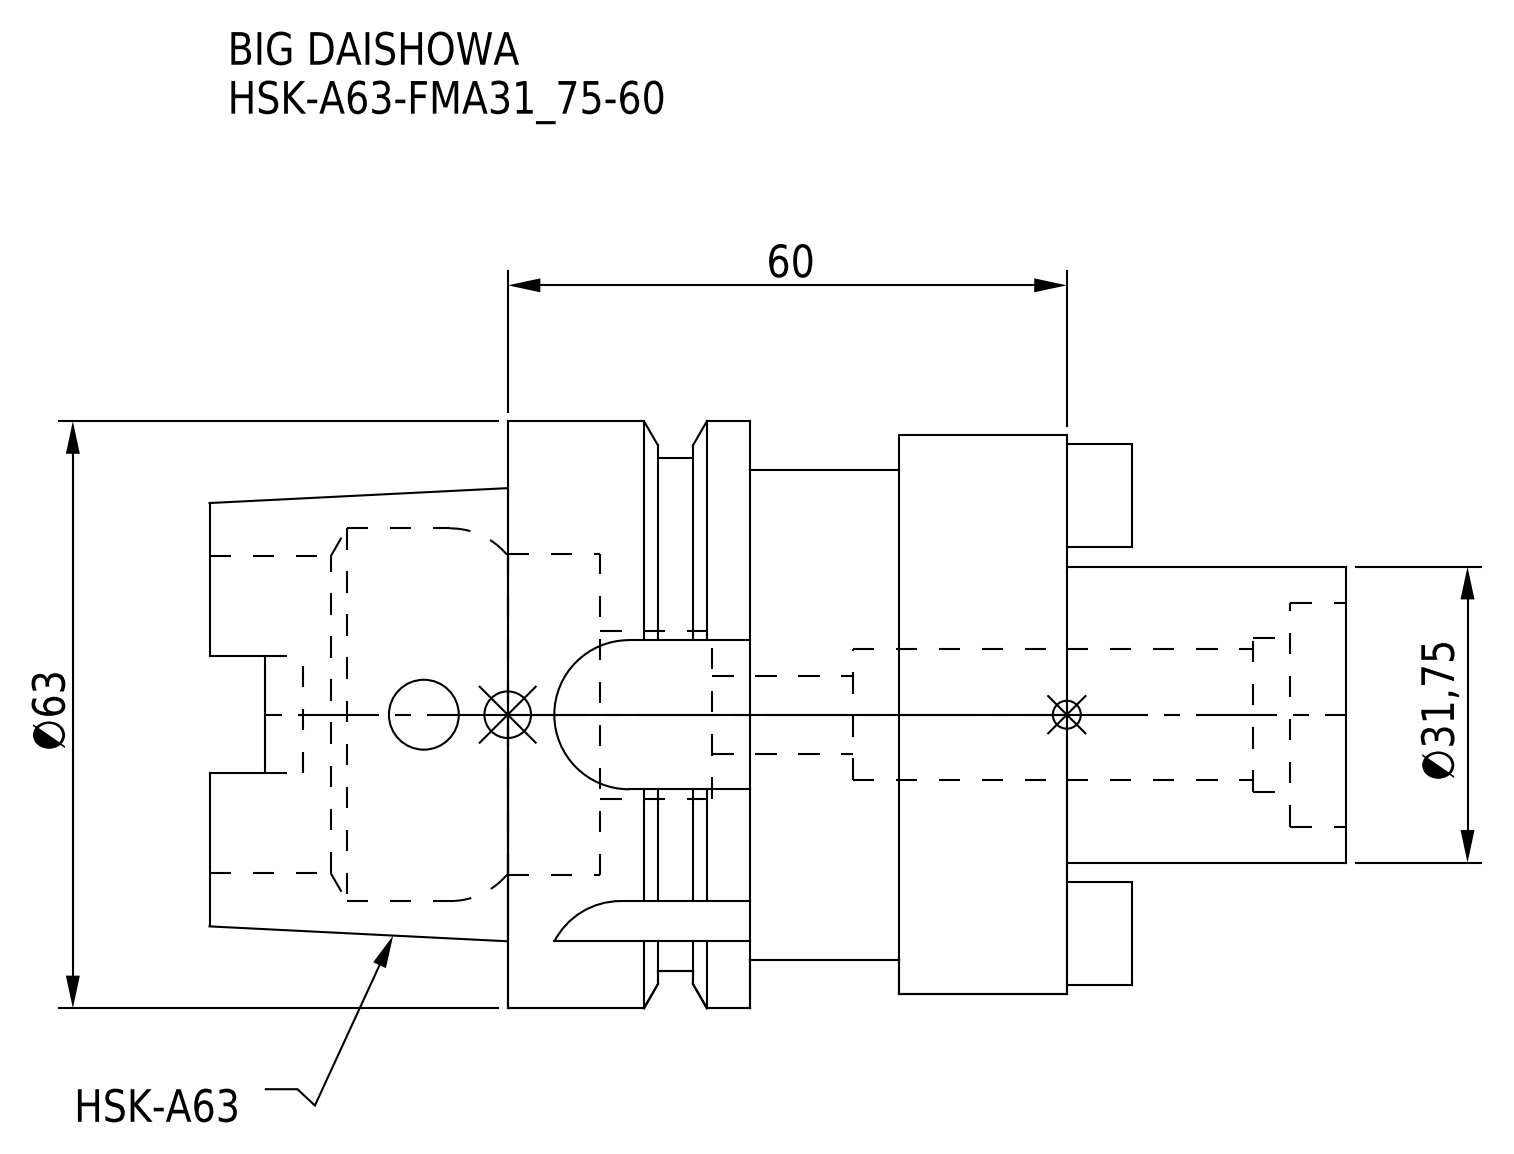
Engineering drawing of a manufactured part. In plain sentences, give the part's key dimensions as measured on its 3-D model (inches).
The part is named "HSK-A63-FMA31_75-60". Its 3-D file was written by "CREO PARAMETRIC BY PTC INC, 2016380 (AUTOMOTIVE_DESIGN)". It is 1 solid with 98 faces: 46 planar, 40 cylindrical and 12 other. Overall it measures 4.803 by 2.48 by 2.48 inches. Its volume is 11.13 cubic inches and its surface area 56.24 square inches. Round holes: 1 of diameter 0.295, 1 of diameter 0.331, 1 of diameter 0.551, 1 of diameter 0.65, 1 of diameter 0.709, 1 of diameter 0.945, 1 of diameter 1.339, 1 of diameter 1.358, 1 of diameter 1.575. Round bosses or shafts: 1 of diameter 2.48, 1 of diameter 2.362, 1 of diameter 2.165, 1 of diameter 2.071, 1 of diameter 1.25. Partial cylindrical surfaces (rounded edges, fillets, slot ends): 2 of radius 0.315, 1 of radius 0.354. The main face-to-face distances are 2.362, 1.024, 2.283, 1.654, 1.339, 0.63, 0.709, 1.97, 0.632, 0.392.
